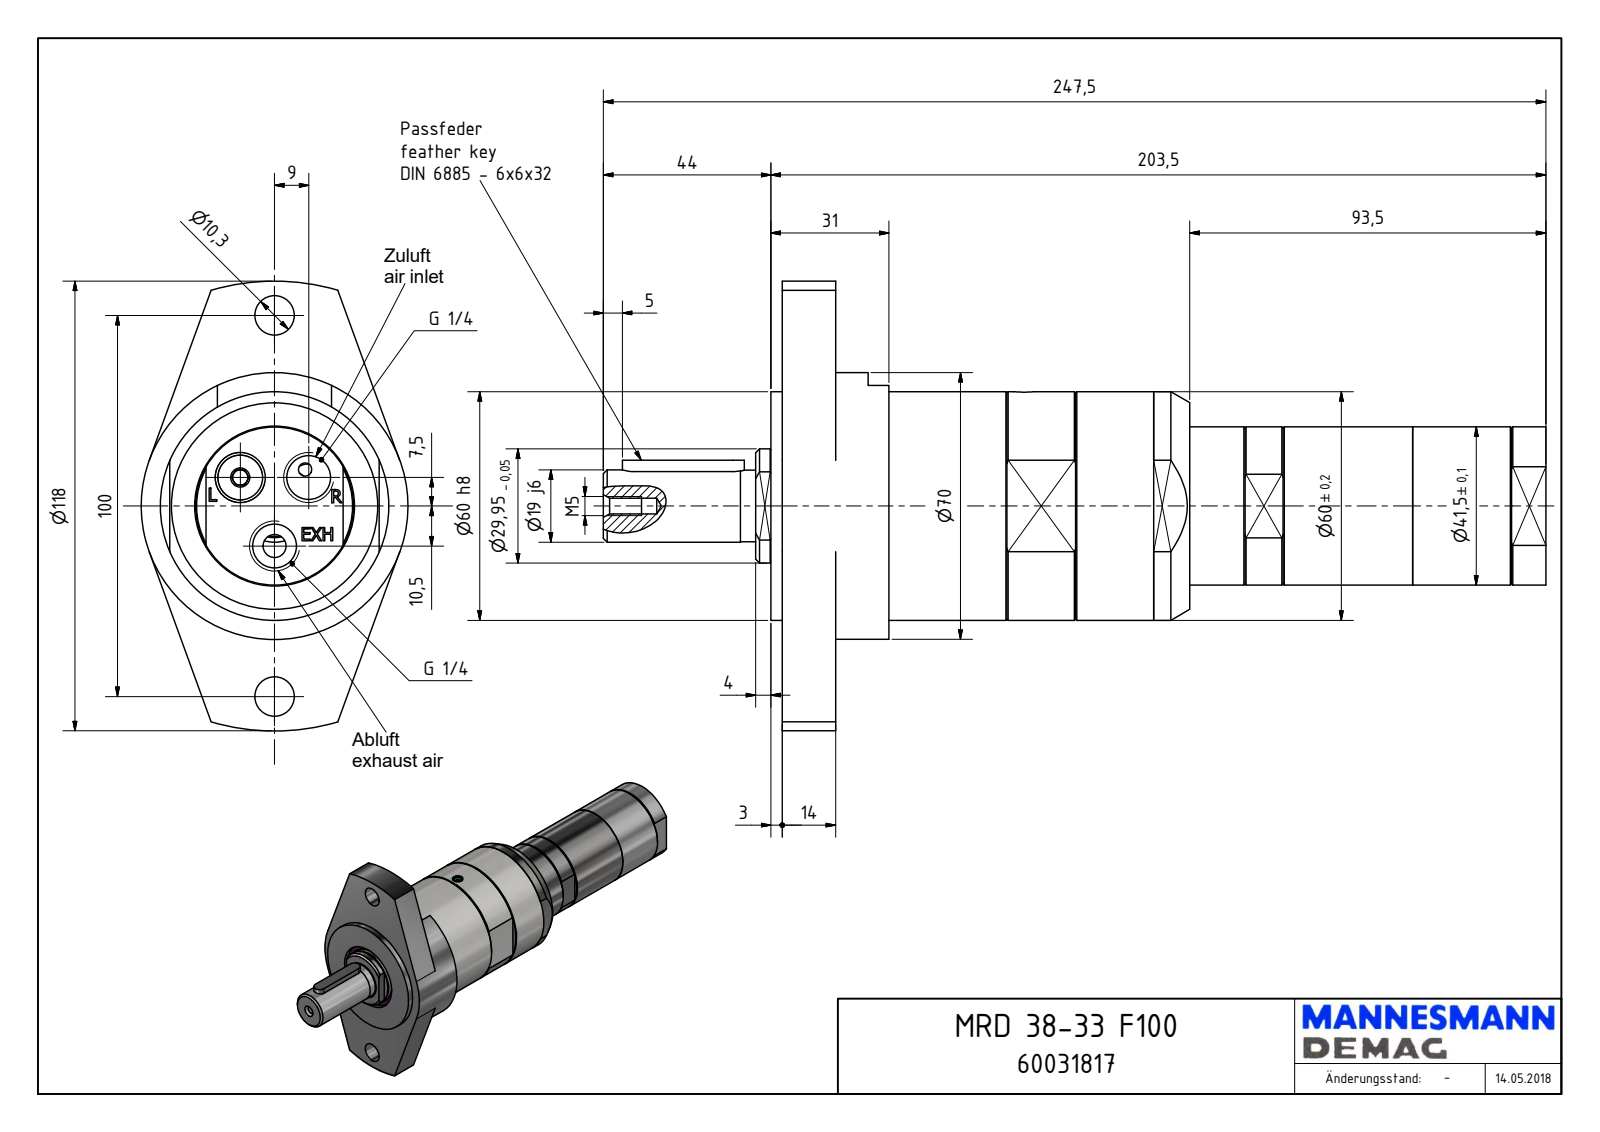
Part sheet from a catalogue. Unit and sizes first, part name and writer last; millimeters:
Units: millimetres
Overall size (bounding box): 247.5 × 118 × 70
Round holes (diameter × count): ⌀11.45 ×3, ⌀4 ×2, ⌀10.3 ×2, ⌀1.55 ×1, ⌀4.13 ×1, ⌀5.5 ×1, ⌀35 ×1, ⌀42 ×1
Round bosses / shafts (diameter × count): ⌀70 ×1, ⌀60 ×1, ⌀55.18 ×1, ⌀41.5 ×1, ⌀38.54 ×1, ⌀29.95 ×1, ⌀19 ×1, ⌀18.8 ×1
Partial cylindrical surfaces — rounded edges, fillets, slot ends (radius × count): R11.68 ×94, R3.5 ×4, R3 ×2, R10.7 ×2, R24.27 ×1, R24.96 ×1, R59 ×1
Main face-to-face distances: 14, 3, 17, 31, 79, 93, 203.5, 200.5, 186.5, 8.5
Hole centre spacings: 11.72, 20.12, 43.44, 50, 58.2, 10.5, 18, 39.5
Volume: 500 447 mm³ · Surface area: 59 245 mm²
Bodies: 1 solid, 517 faces (226 planar, 245 cylindrical, 46 other)
Part name (STEP PRODUCT): MRD 38-33 F100_60031817
STEP written by: Autodesk Inventor 2018 (AUTOMOTIVE_DESIGN)
